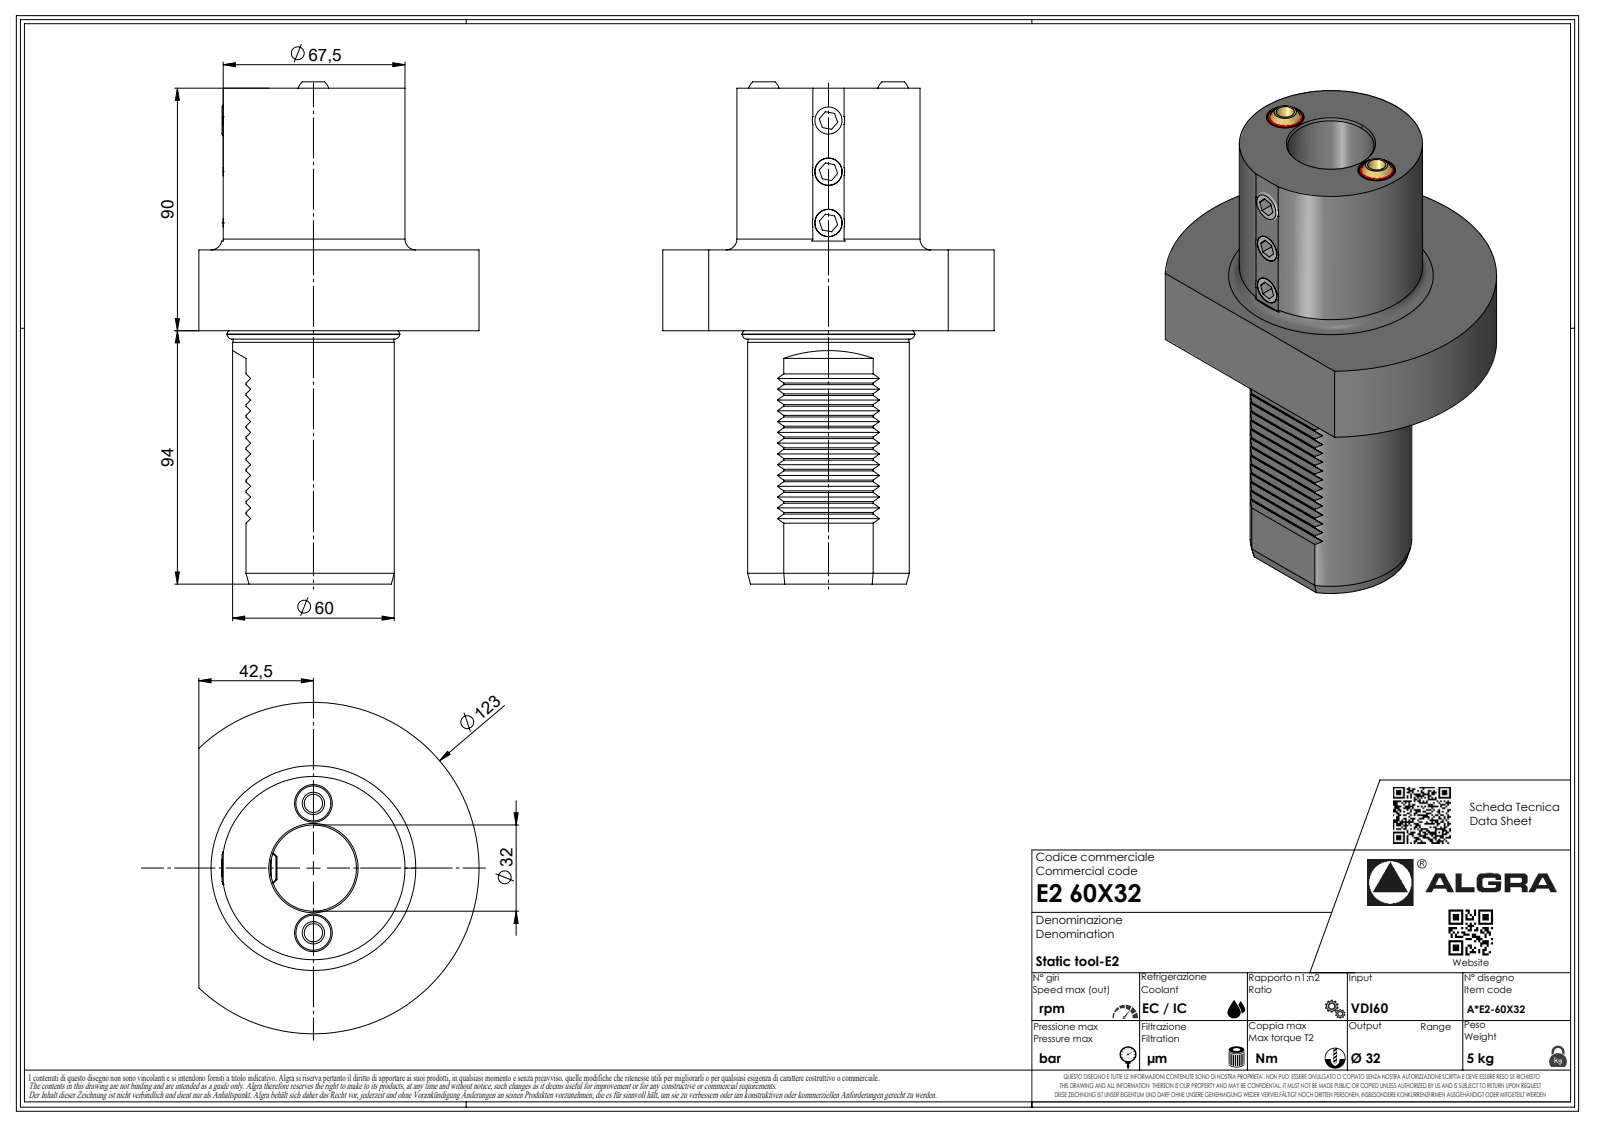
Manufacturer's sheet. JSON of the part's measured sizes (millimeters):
{"part_name": "E260X32", "step_written_by": "SolidWorks 2023 (AUTOMOTIVE_DESIGN)", "units": "millimeters", "bodies": {"solids": 1, "faces": 296, "planar": 198, "cylindrical": 42, "other": 56}, "overall_size": [186.37, 123, 104], "volume_mm3": 790335, "surface_area_mm2": 64511, "round_holes": [[10.07, 2], [2.1, 1], [11.47, 1], [32, 1]], "round_bosses_or_shafts": [[68, 1], [64.19, 1], [60, 1], [6.37, 1], [1.7, 1]], "partial_cylinders_radius": [[0.33, 7], [0.52, 7], [3.7, 7], [6, 3], [0.21, 1], [61.5, 1]], "face_to_face_distances": [30, 60, 90, 184, 124, 94, 2.83, 14.14, 11.31, 5.66], "hole_center_spacings": [19, 21.64, 38, 40.03, 58.81]}
